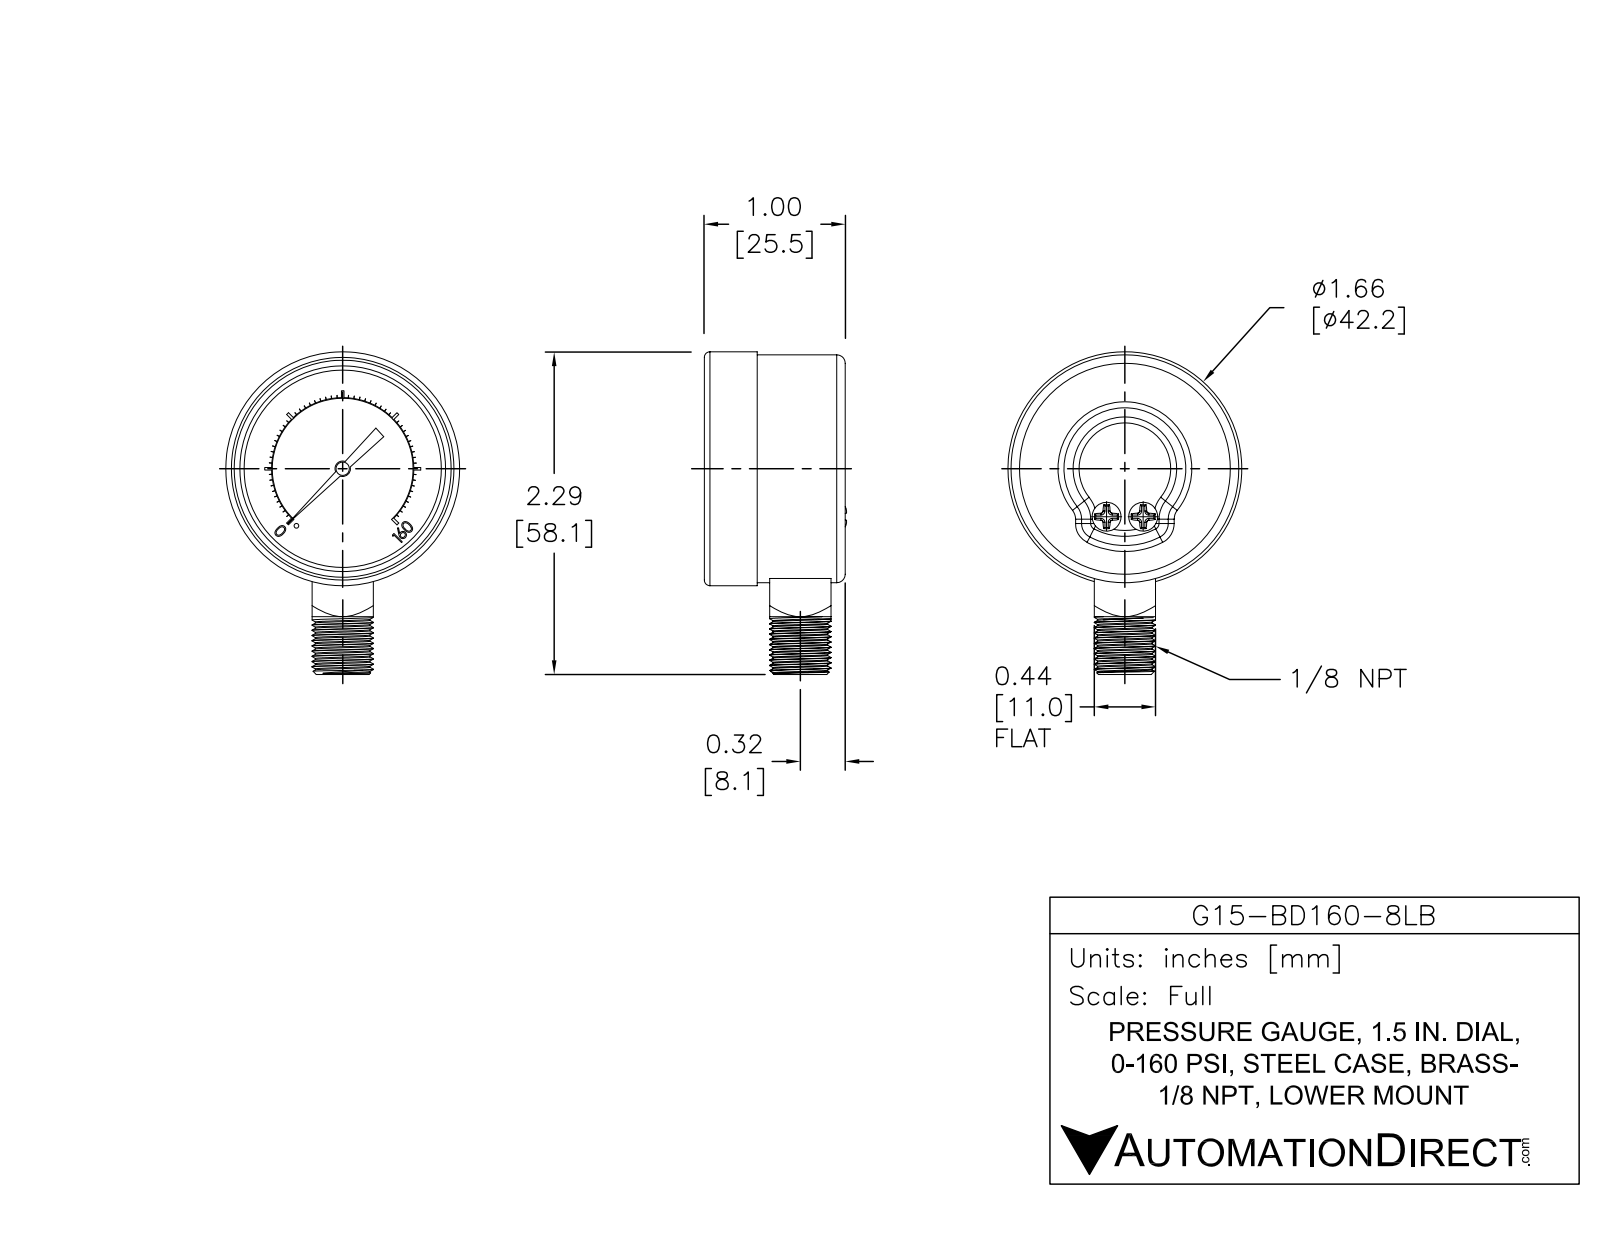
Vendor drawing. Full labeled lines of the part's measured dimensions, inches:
Part name (STEP PRODUCT): G15-BD160-8LB
STEP written by: SolidWorks 2021 (AUTOMOTIVE_DESIGN)
Units: inches
Bodies: 1 solid, 420 faces (273 planar, 82 cylindrical, 65 other)
Overall size (bounding box): 2.29 × 1.66 × 1.01
Volume: 1.682 in³ · Surface area: 12.05 in²
Round holes (diameter × count): ⌀0.14 ×1, ⌀1.4 ×1
Round bosses / shafts (diameter × count): ⌀0.205 ×2, ⌀1.66 ×1, ⌀1.617 ×1, ⌀0.435 ×1, ⌀0.11 ×1, ⌀0.095 ×1, ⌀0.033 ×1
Partial cylindrical surfaces — rounded edges, fillets, slot ends (radius × count): R0.06 ×4, R0.5 ×1, R0.505 ×1
Main face-to-face distances: 0.71, 0.1, 0.61, 0.435, 0.96, 0.86, 0.25, 0.04, 0.625, 0.525
